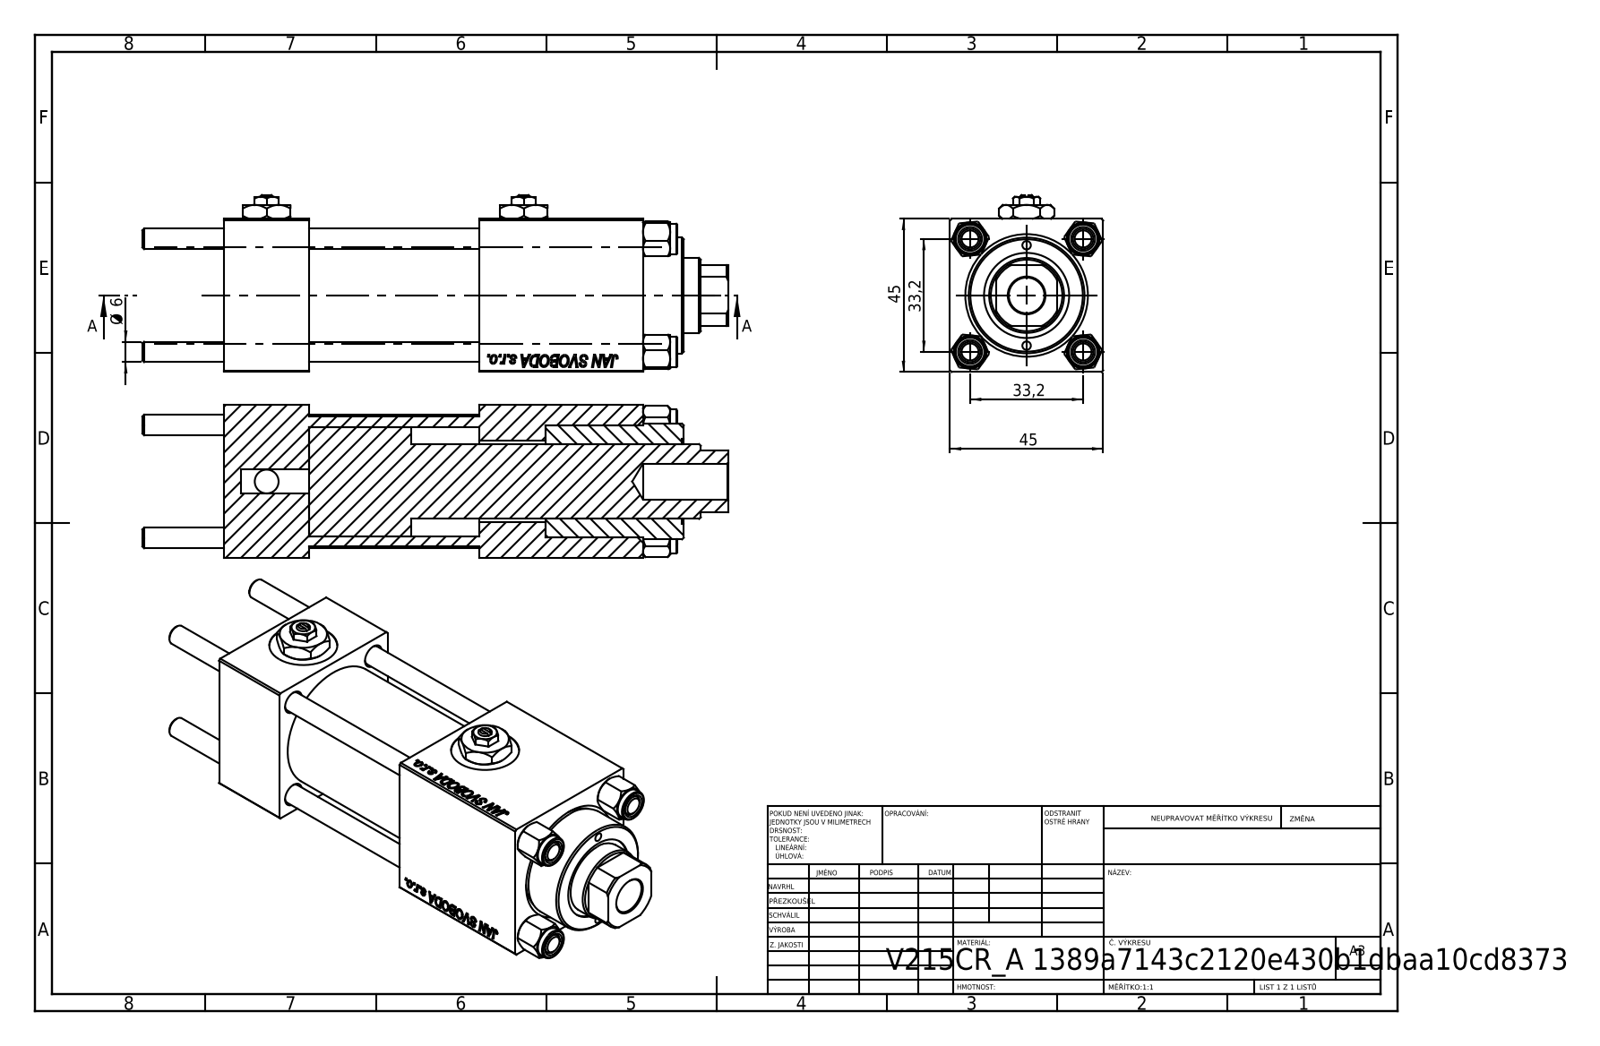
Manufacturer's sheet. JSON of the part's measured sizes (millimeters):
{"part_name": "V215CR_BODY_A; NUT_M5; V215CR_VCP; Zatka_pro_OIL_PORT (+2 more)", "step_written_by": "SolidWorks 2019 (CONFIG_CONTROL_DESIGN)", "units": "millimeters", "bodies": {"solids": 13, "faces": 1238, "planar": 568, "cylindrical": 92, "other": 578}, "overall_size": [172, 52, 45], "volume_mm3": 212553, "surface_area_mm2": 79149, "round_holes": [[6, 4], [2.5, 2], [7, 2], [13.16, 2], [20, 2], [10.5, 1], [22, 1], [24, 1], [25, 1], [32, 1], [33, 1]], "round_bosses_or_shafts": [[9, 4], [38, 1], [34, 1]], "partial_cylinders_radius": [[10.5, 1]], "face_to_face_distances": [45, 25, 123, 50, 75, 98, 48, 44.8, 94.3, 69.3], "hole_center_spacings": [16.7, 23.48, 33.2, 35.47, 14.75, 46.95, 29.5, 75.5]}
